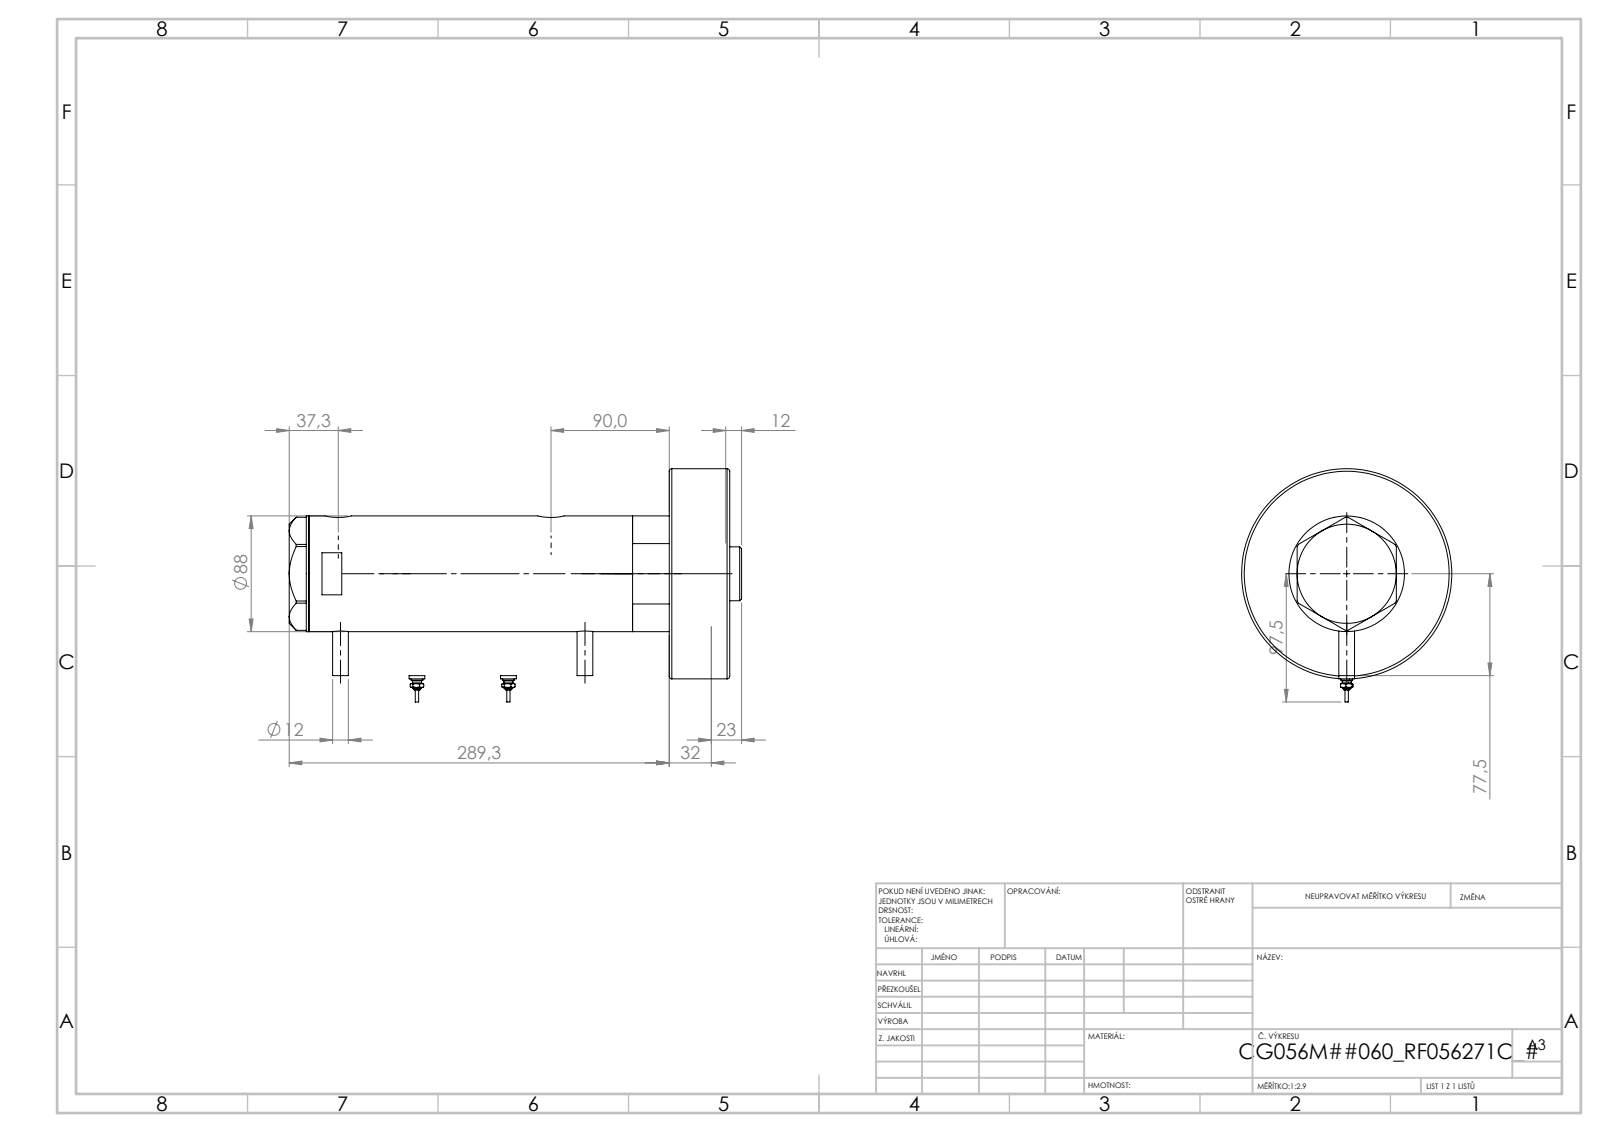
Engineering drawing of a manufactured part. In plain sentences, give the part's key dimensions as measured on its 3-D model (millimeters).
The part is named "V270CG_BACK; Switch; V270CG_VC; V270CG_271C (+2 more)". Its 3-D file was written by "SolidWorks 2019 (CONFIG_CONTROL_DESIGN)". It is 7 solids with 223 faces: 82 planar, 73 cylindrical and 68 other. Overall it measures 344.3 by 177.5 by 160 millimeters. Its volume is 2 555 000 cubic millimeters and its surface area 320 036 square millimeters. Round holes: 2 of diameter 12.5, 2 of diameter 13.16, 2 of diameter 20, 1 of diameter 14.5, 1 of diameter 42, 1 of diameter 43.5, 1 of diameter 56, 1 of diameter 60, 1 of diameter 75, 1 of diameter 80. Round bosses or shafts: 4 of diameter 12, 2 of diameter 9, 2 of diameter 7, 2 of diameter 4.5, 2 of diameter 2.5, 1 of diameter 160, 1 of diameter 88, 1 of diameter 73. The main face-to-face distances are 46, 274.3, 320.3, 184.4, 89.9, 135.9, 294.3, 26, 158.4, 248.3. The hole center spacings are 1.7, 25.8, 160.3, 162, 186.1, 187.8.
